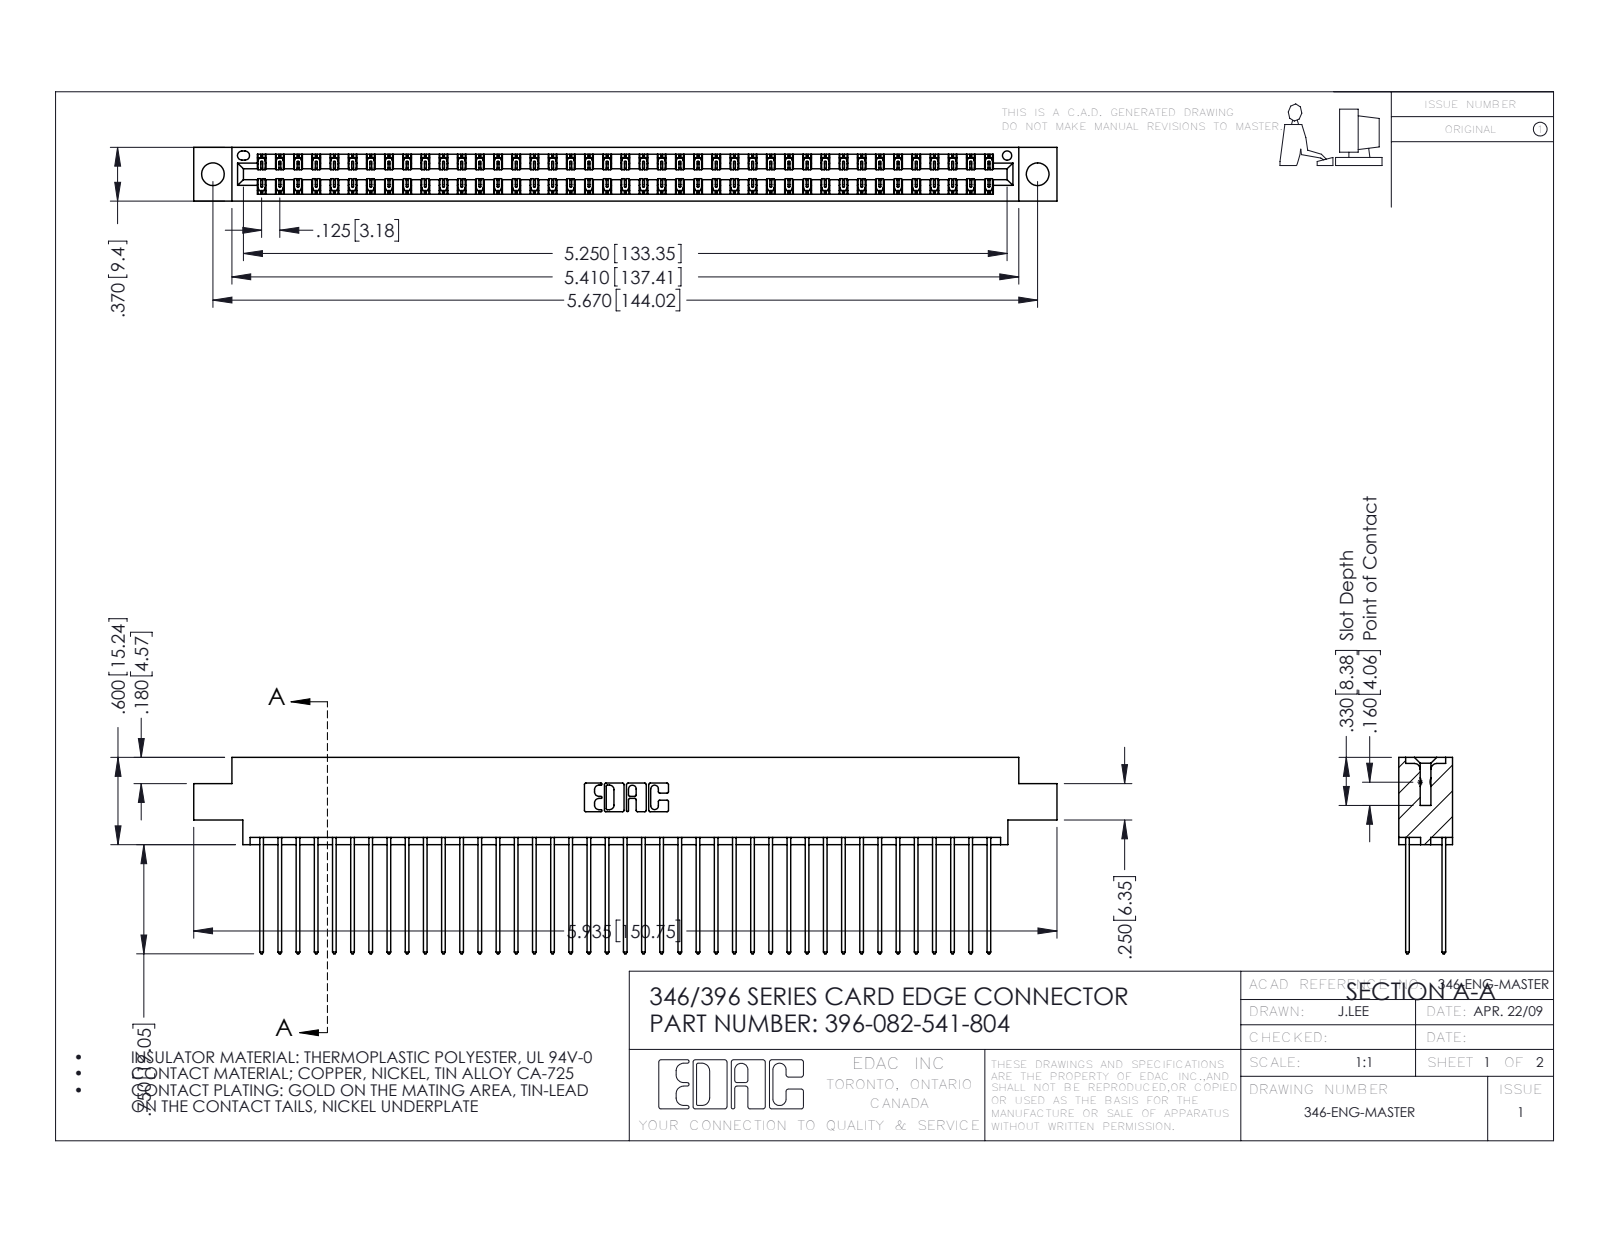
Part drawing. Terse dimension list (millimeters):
name: 396-082-541-804; 346 Part_0.170 Offset - 0.156 Dia-TH; 345-292-001_345-293-141
written by: SolidWorks 2016 (CONFIG_CONTROL_DESIGN)
unit: mm
bodies: 83 solids, 4390 faces (2950 planar, 1440 cylindrical, 0 other)
size: 150.7 × 34.3 × 9.4
volume: 14 900 mm³; area: 22 740 mm²
holes: 2× ⌀4, 1× ⌀1.6
rounds: 123× R0.2, 82× R0.3, 22× R0.3, 6× R0.2, 6× R0.8, 3× R0.7, 2× R0.4, 2× R0.6
face distances: 1.2, 8.2, 6.4, 1.8, 7.6, 0.6, 9.4, 7, 5.7, 3.8
hole spacings: 6.2, 138.7, 144
